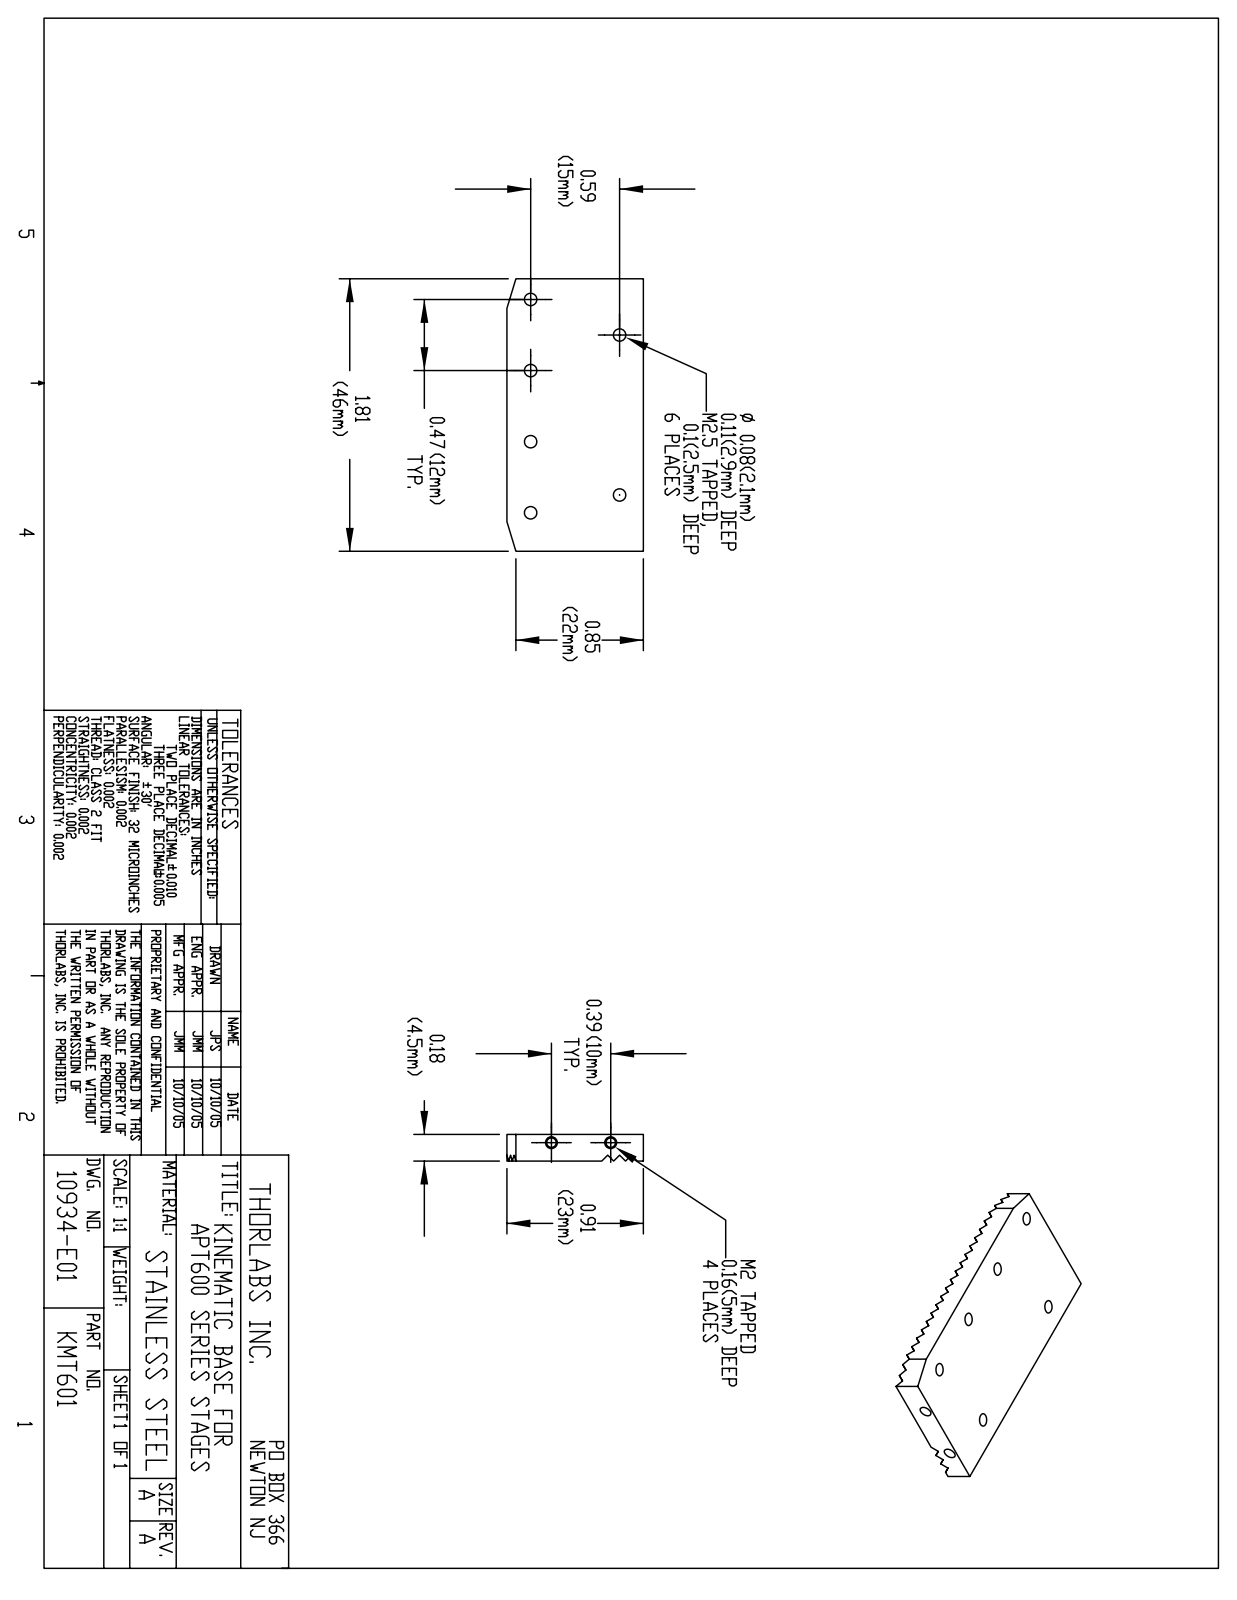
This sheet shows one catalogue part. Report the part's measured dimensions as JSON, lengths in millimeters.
{"part_name": "10934-E0W", "step_written_by": "SolidWorks 2007 (AUTOMOTIVE_DESIGN)", "units": "millimeters", "bodies": {"solids": 0, "faces": 128, "planar": 85, "cylindrical": 20, "other": 23}, "overall_size": [46, 23, 4.5], "round_holes": [[2.1, 6], [1.6, 2]], "face_to_face_distances": [1.4, 2.8, 7.1, 4.2, 9.9, 14.1, 11.3, 5.7, 8.5, 1.4], "hole_center_spacings": [12, 16.2, 24, 10, 15.3, 17.5, 23.4, 25.8]}
